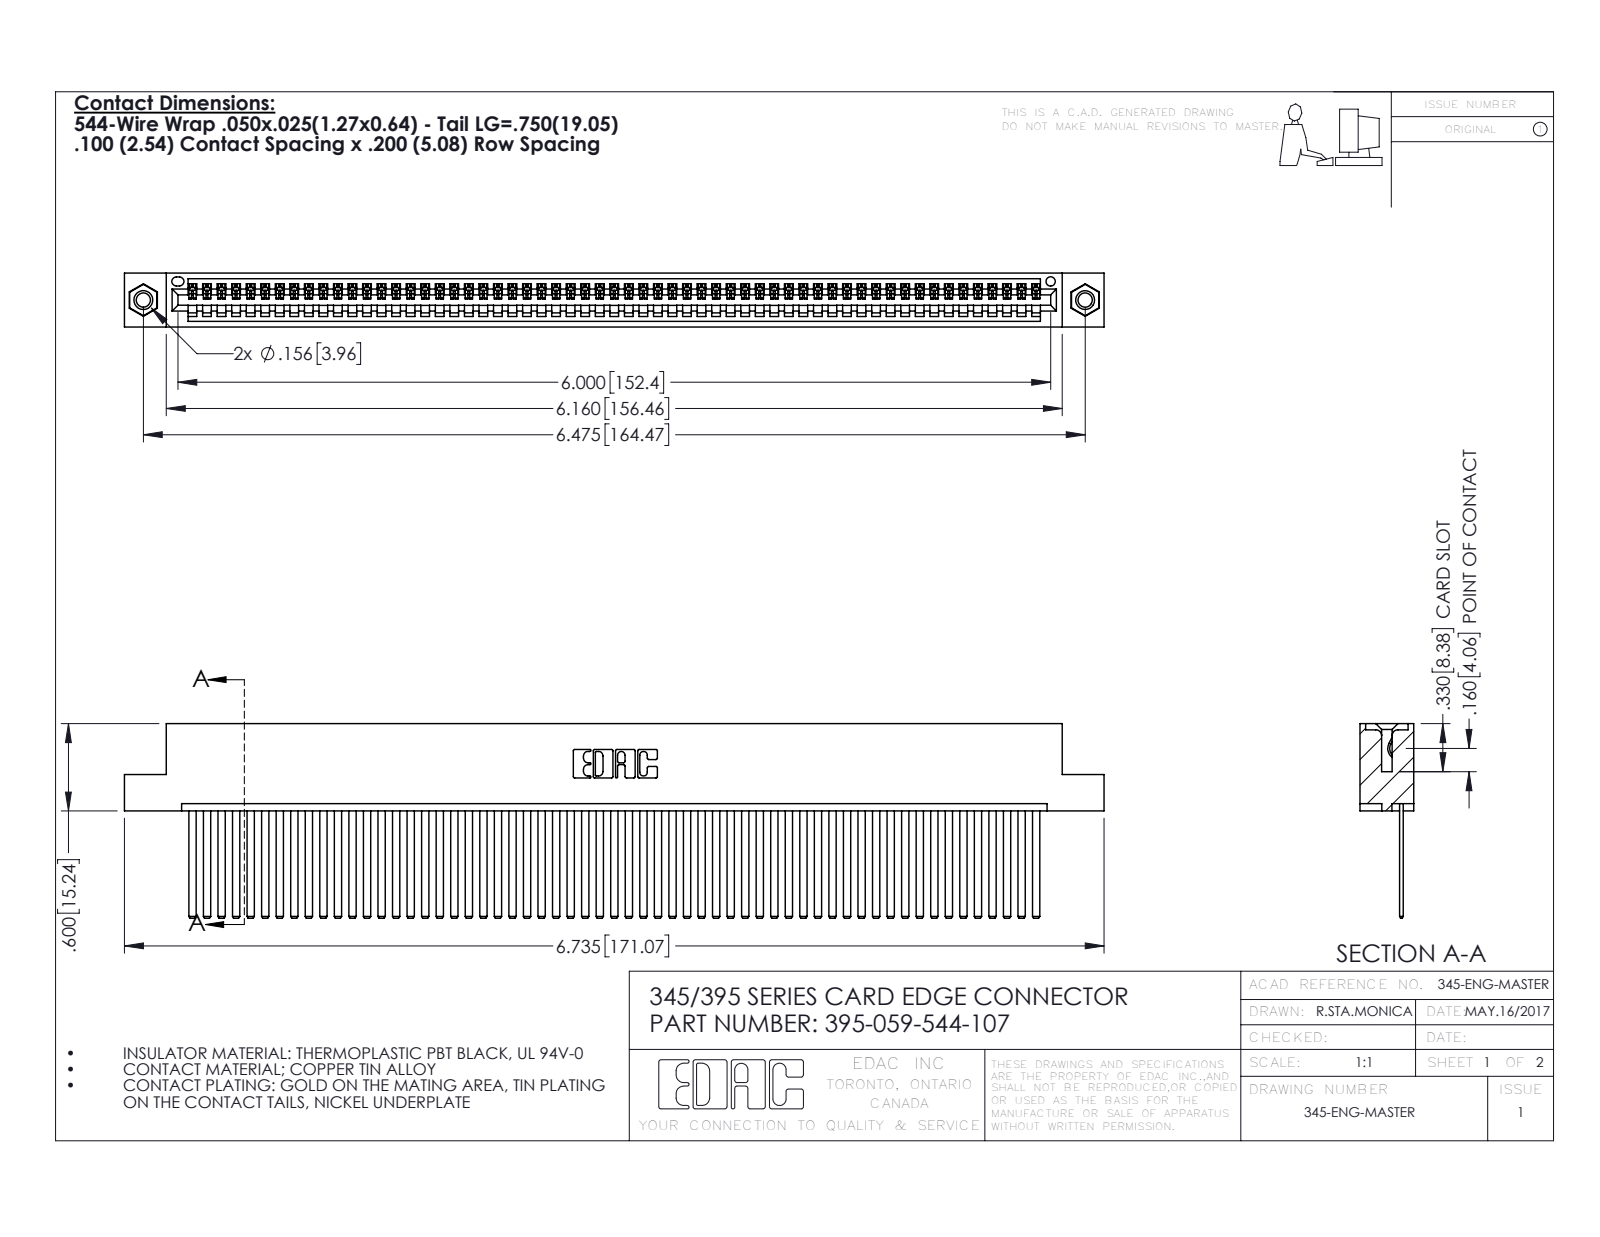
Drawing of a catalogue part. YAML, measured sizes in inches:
part_name: "345-250-001_345-250-005-103; 395-059-544-107; 345-292-001_345-293-144; 345 Part_Flush Mounting Lugs - 0.156 Dia-TI"
step_written_by: "SolidWorks 2016 (CONFIG_CONTROL_DESIGN)"
units: inches
bodies: {solids: 62, faces: 3254, planar: 2236, cylindrical: 1002, other: 16}
overall_size: [6.735, 1.337, 0.37]
volume: 1.041
surface_area: 38.72
round_holes:
  - {diameter: 0.098, count: 2}
  - {diameter: 0.125, count: 2}
  - {diameter: 0.156, count: 2}
  - {diameter: 0.064, count: 1}
round_bosses_or_shafts:
  - {diameter: 0.155, count: 2}
partial_cylinders:
  - {radius: 0.006, count: 118}
  - {radius: 0.01, count: 22}
  - {radius: 0.007, count: 6}
  - {radius: 0.031, count: 6}
  - {radius: 0.026, count: 3}
  - {radius: 0.031, count: 2}
  - {radius: 0.04, count: 2}
  - {radius: 0.014, count: 1}
face_to_face_distances: [0.072, 0.298, 0.025, 0.098, 0.272, 0.37, 0.2, 0.225, 0.149, 0.072]
hole_center_spacings: [0.27, 6.239, 6.475]
